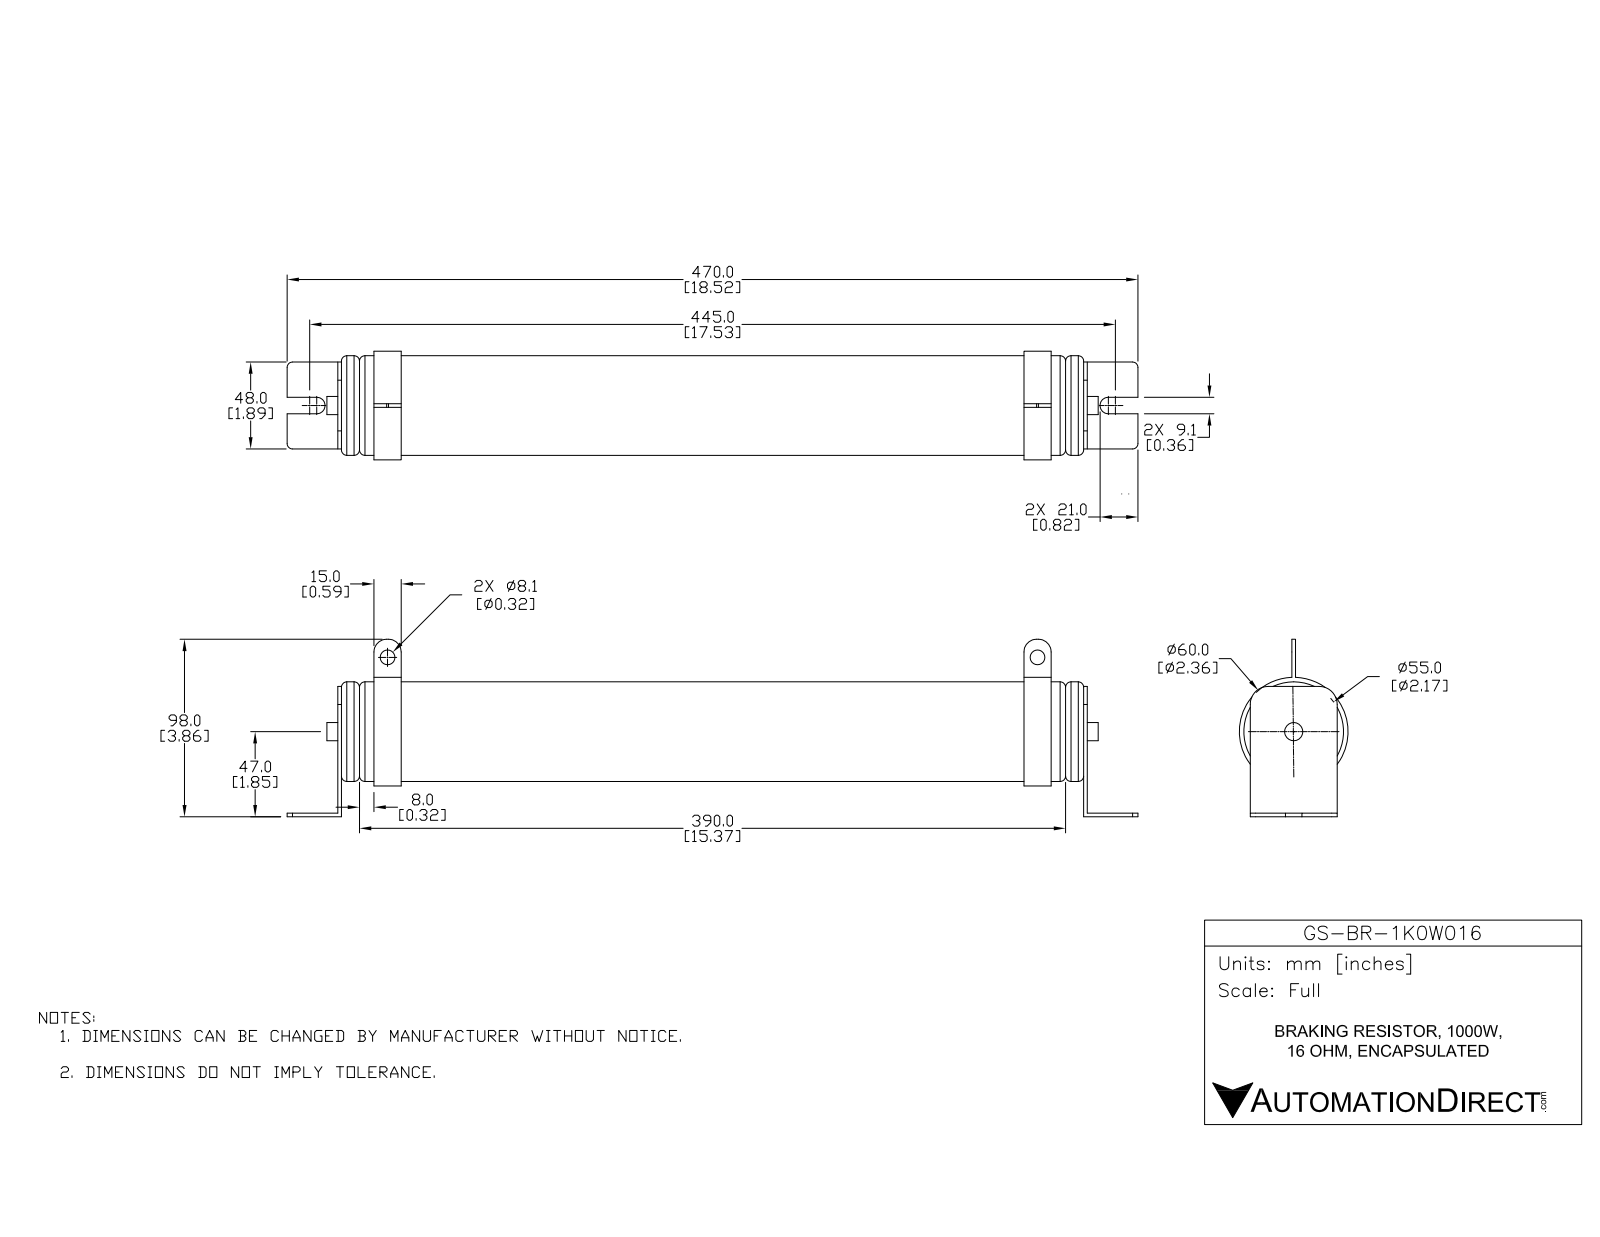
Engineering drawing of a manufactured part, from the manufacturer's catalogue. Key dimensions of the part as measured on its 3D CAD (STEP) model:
Part name (STEP PRODUCT): GS-BR-1K0W016
STEP written by: SolidWorks 2015 (AUTOMOTIVE_DESIGN)
Units: inches
Bodies: 2 solids, 91 faces (41 planar, 38 cylindrical, 12 other)
Overall size (bounding box): 18.504 × 3.858 × 2.362
Volume: 61.39 in³ · Surface area: 143.2 in²
Round holes (diameter × count): ⌀0.319 ×2
Round bosses / shafts (diameter × count): ⌀2.362 ×1, ⌀2.166 ×1, ⌀2.165 ×1, ⌀0.394 ×1
Partial cylindrical surfaces — rounded edges, fillets, slot ends (radius × count): R0.118 ×4, R0.276 ×4, R0.179 ×2, R0.394 ×2
Main face-to-face distances: 0.079, 16.299, 16.22, 16.142, 1.378, 14.921, 1.299, 14.843, 0.787, 15.512
Hole centre spacings: 14.134
